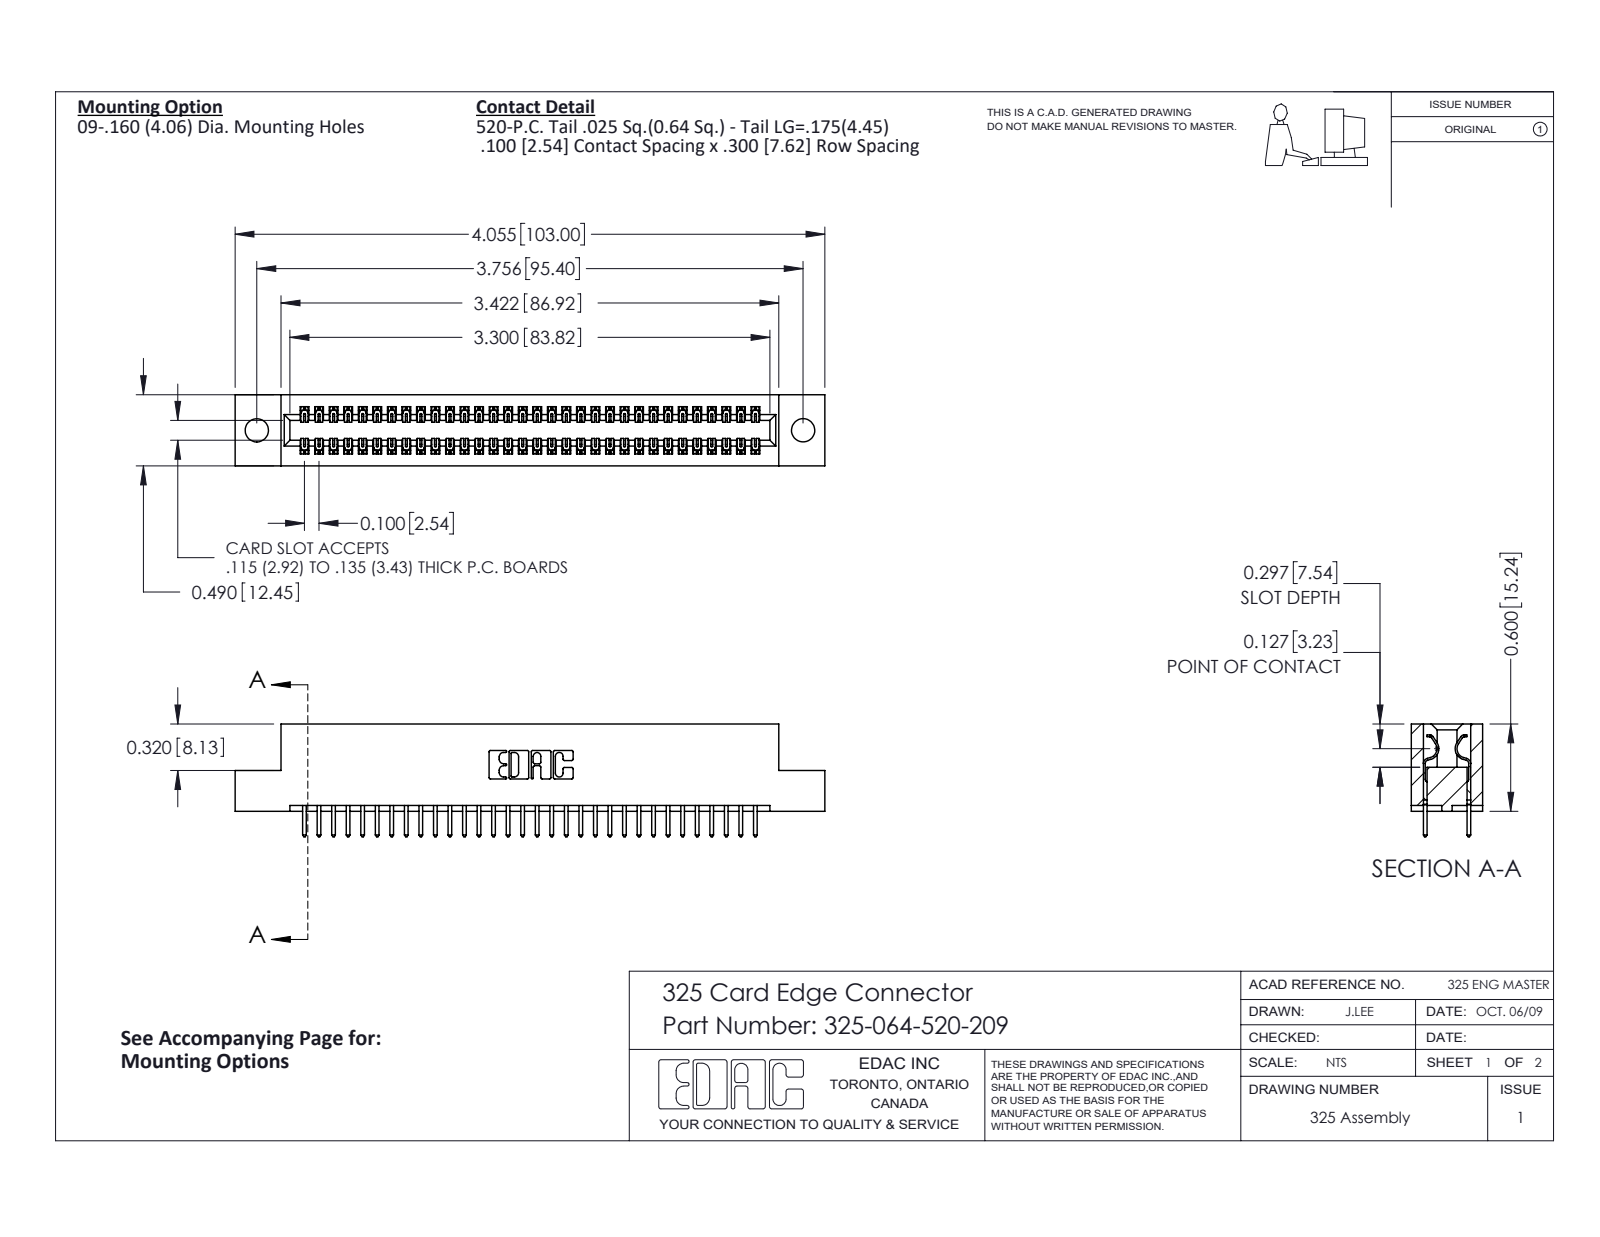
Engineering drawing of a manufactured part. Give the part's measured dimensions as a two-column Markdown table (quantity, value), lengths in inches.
| quantity | value |
| --- | --- |
| part name | 325 Part_.160 TH; 325-064-520-209; 325-292-001_325-293-120 |
| STEP written by | SolidWorks 2016 (CONFIG_CONTROL_DESIGN) |
| units | inches |
| bodies | 65 solids, 3442 faces (2374 planar, 1068 cylindrical, 0 other) |
| overall size | 4.055 × 0.775 × 0.49 |
| volume | 0.791 in³ |
| surface area | 23.63 in² |
| round holes (diameter × count) | 0.16 × 2 |
| partial cylindrical surfaces (radius × count) | 0.006 × 96, 0.01 × 64, 0.01 × 22, 0.007 × 6, 0.031 × 6, 0.026 × 3, 0.014 × 2, 0.022 × 2 |
| main face-to-face distances | 0.083, 0.407, 0.3, 0.49, 0.107, 0.383, 0.025, 0.325, 0.275, 0.04 |
| hole center spacings | 3.756 |
